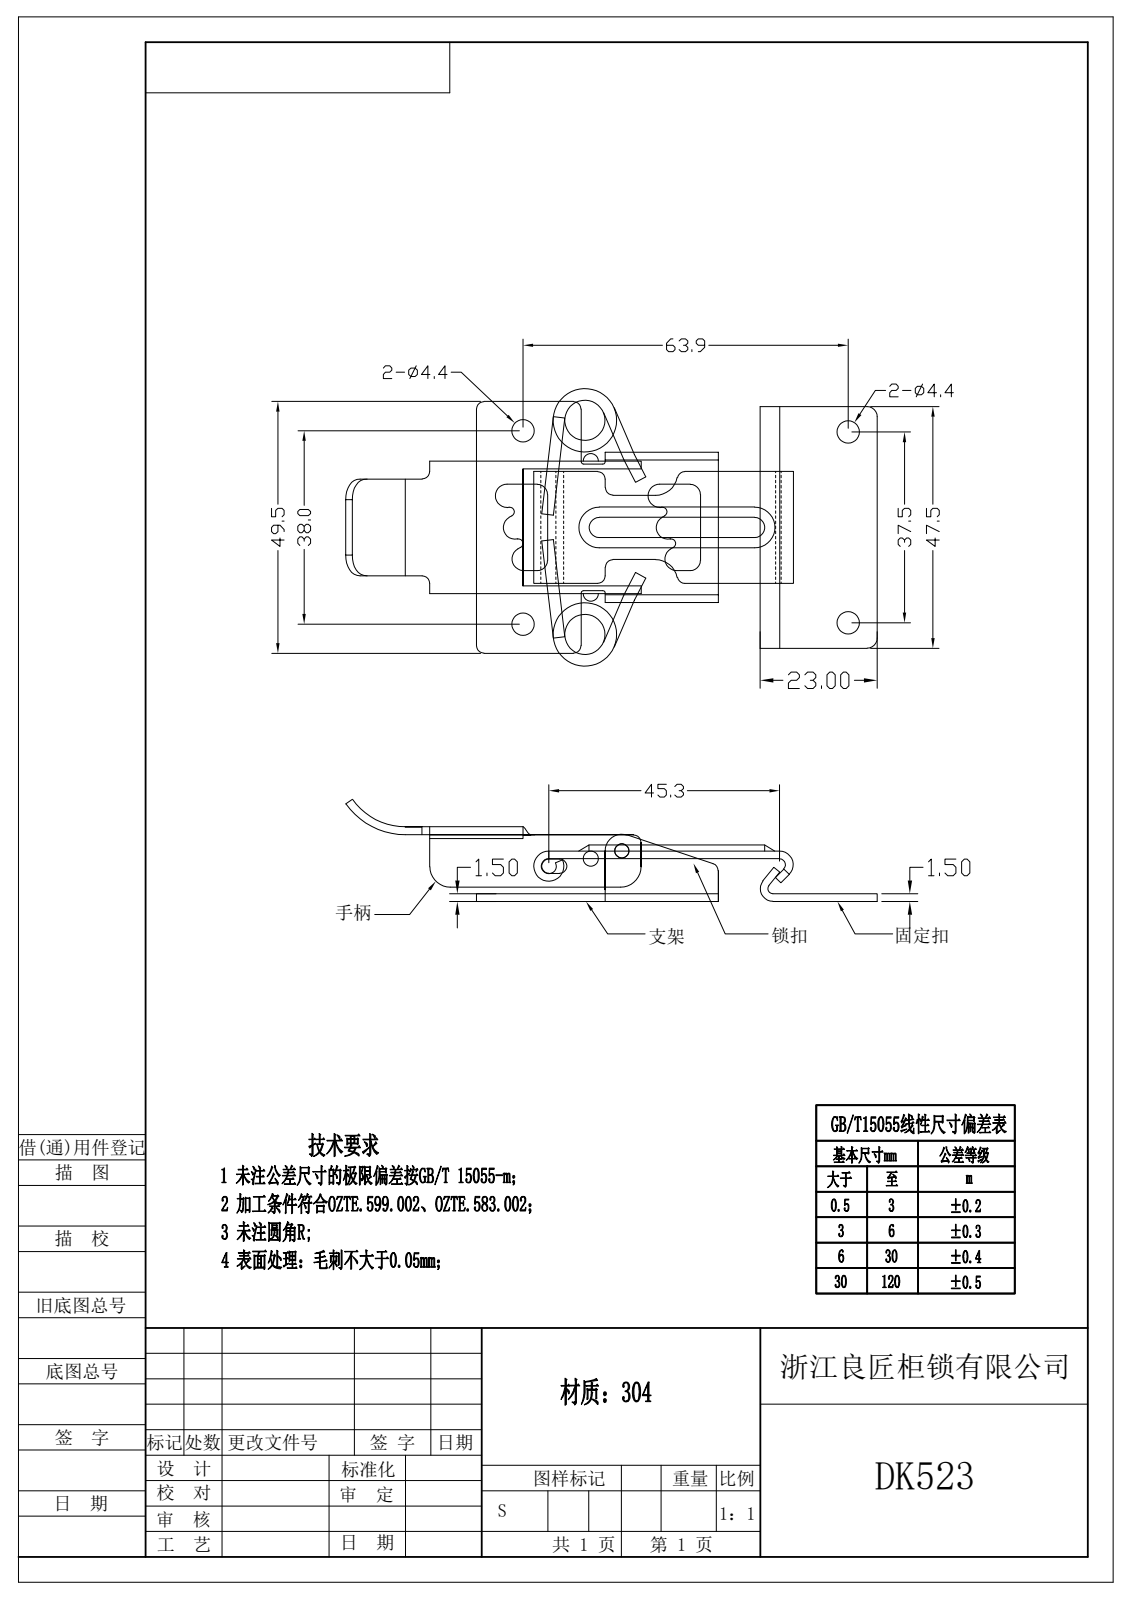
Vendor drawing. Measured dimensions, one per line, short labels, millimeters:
name: 图块 01
written by: Rhino 8.5 (CONFIG_CONTROL_DESIGN)
unit: mm
bodies: 4 solids, 199 faces (87 planar, 93 cylindrical, 19 other)
size: 104.95 × 52.01 × 20.06
volume: 4 621 mm³; area: 15 108 mm²
holes: 4× ⌀4.4, 1× ⌀2.8, 1× ⌀3
bosses: 4× ⌀2.3, 1× ⌀6, 1× ⌀0.6
rounds: 16× R1.5, 8× R2, 6× R2.3, 4× R0.5, 4× R0.9, 2× R0.2, 2× R1.4, 2× R1.7
face distances: 1.5, 0.99, 8.41, 7.42, 2.49, 0.51, 24.5, 1.76, 26.26, 6.91
hole spacings: 64.46, 74.7, 14.62, 37.5, 38
